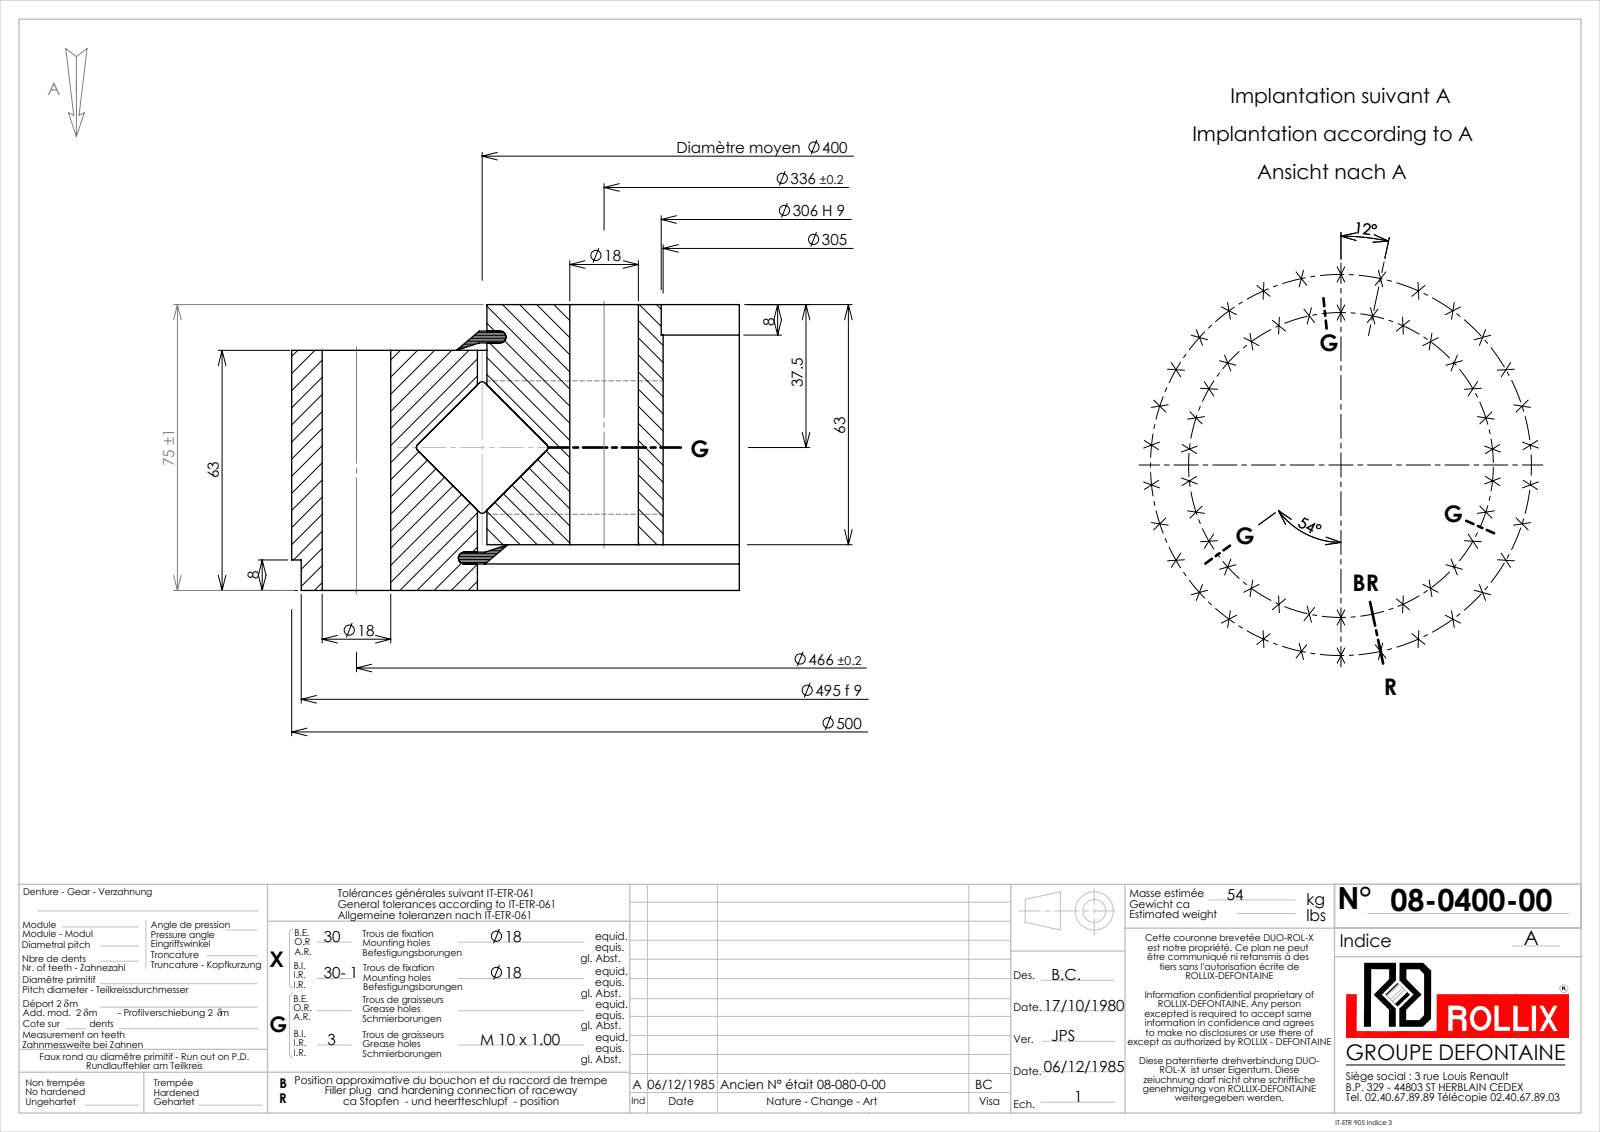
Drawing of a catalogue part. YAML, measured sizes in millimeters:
part_name: "08-0400-00"
step_written_by: "SolidWorks 2016 (CONFIG_CONTROL_DESIGN)"
units: millimeters
bodies: {solids: 5, faces: 204, planar: 16, cylindrical: 146, other: 42}
overall_size: [500, 500, 75]
volume: 5956000
surface_area: 873333
round_holes:
  - {diameter: 18, count: 59}
  - {diameter: 9, count: 3}
  - {diameter: 305, count: 1}
  - {diameter: 306, count: 1}
  - {diameter: 402.5, count: 1}
round_bosses_or_shafts:
  - {diameter: 500, count: 1}
  - {diameter: 495, count: 1}
  - {diameter: 397.5, count: 1}
  - {diameter: 25, count: 1}
face_to_face_distances: [63, 12, 51, 75, 10.05, 64.95, 1.95, 52.95, 6.95, 68.05]
hole_center_spacings: [377, 48.71, 96.89, 273.91, 403.57, 425.71, 144, 233]
